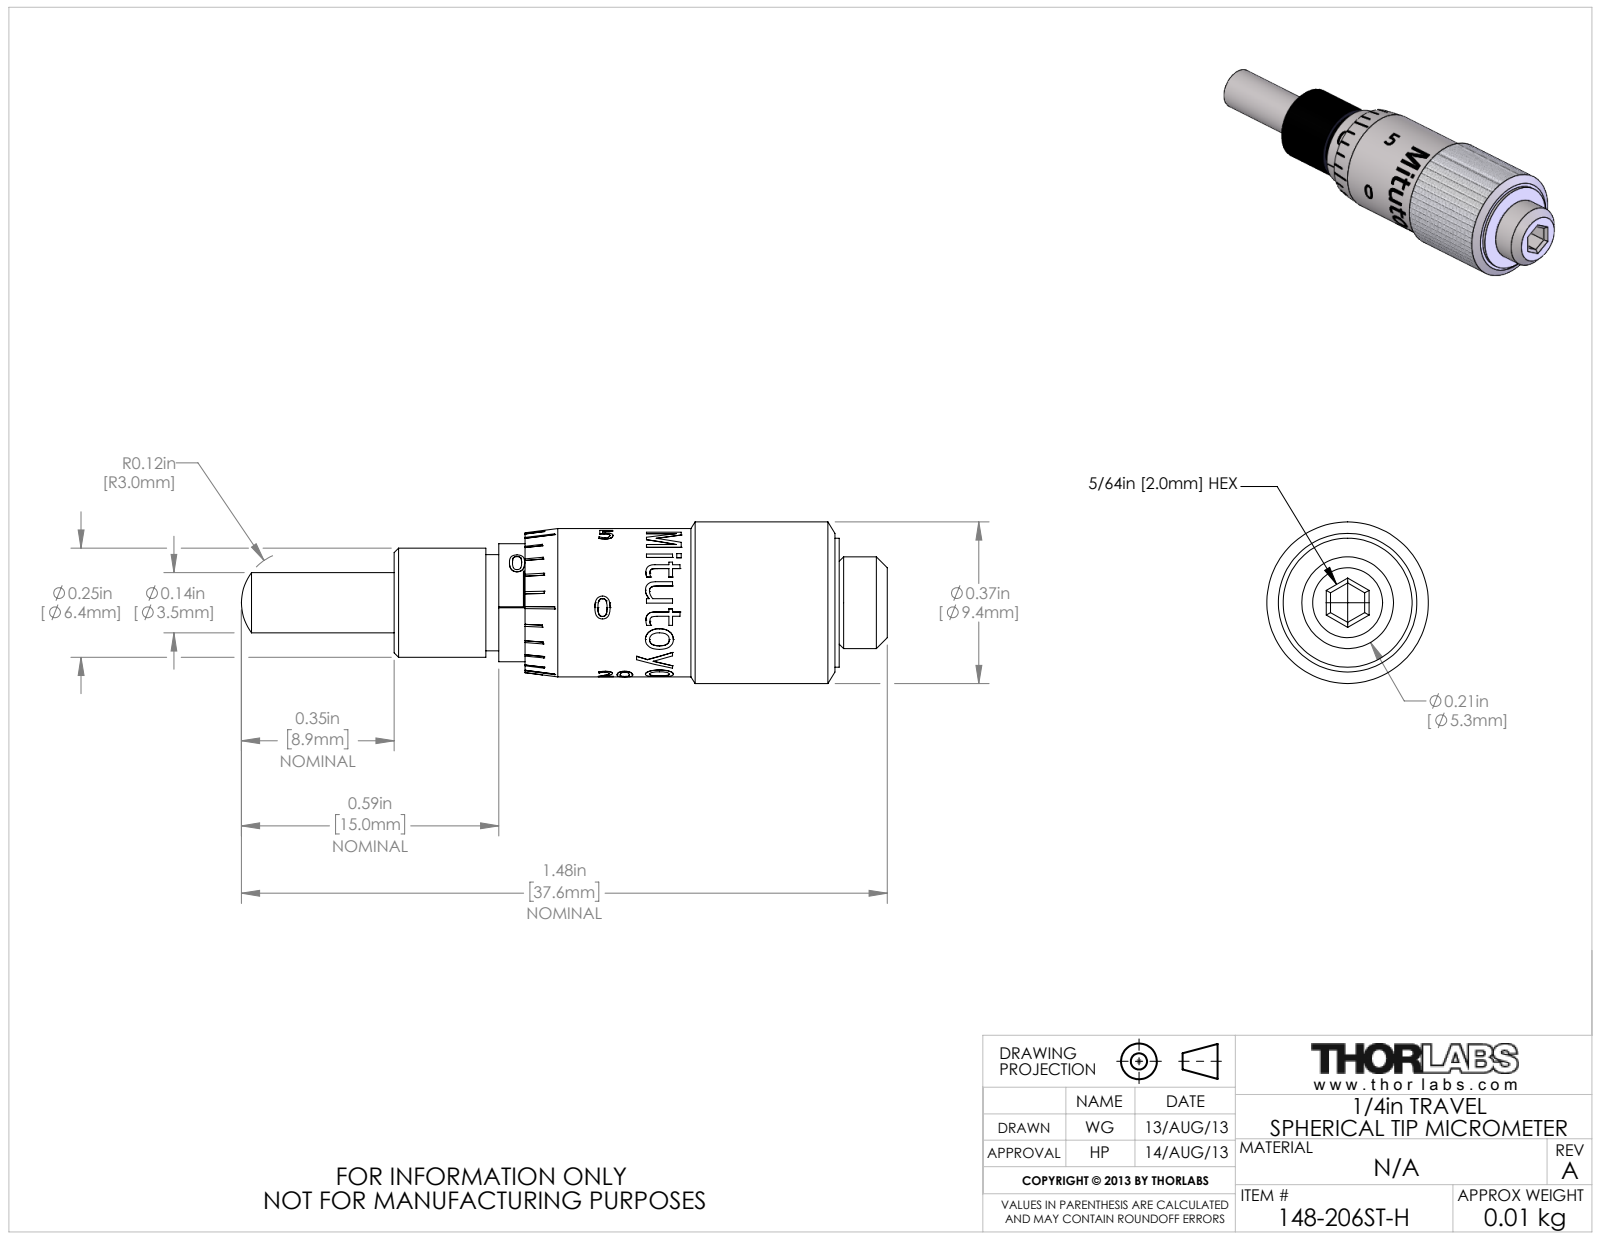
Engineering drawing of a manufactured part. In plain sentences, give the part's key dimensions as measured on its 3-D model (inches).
The part is named "TTN017215-E0W". Its 3-D file was written by "SolidWorks 2012 (AUTOMOTIVE_DESIGN)". It is 2 solids with 416 faces: 178 planar, 72 cylindrical and 166 other. Overall it measures 1.48 by 0.37 by 0.37 inches. Its volume is 0.093 cubic inches and its surface area 1.653 square inches. Round holes: 1 of diameter 0.091. Round bosses or shafts: 1 of diameter 0.37, 1 of diameter 0.34, 1 of diameter 0.295, 1 of diameter 0.27, 1 of diameter 0.25, 1 of diameter 0.22, 1 of diameter 0.21, 1 of diameter 0.138. Partial cylindrical surfaces (rounded edges, fillets, slot ends): 5 of radius 0.165, 5 of radius 0.169, 1 of radius 0.135, 1 of radius 0.17. The main face-to-face distances are 1.02, 0.3, 0.72, 0.06, 0.24, 0.78, 0.21, 0.8, 1.13, 0.89.
